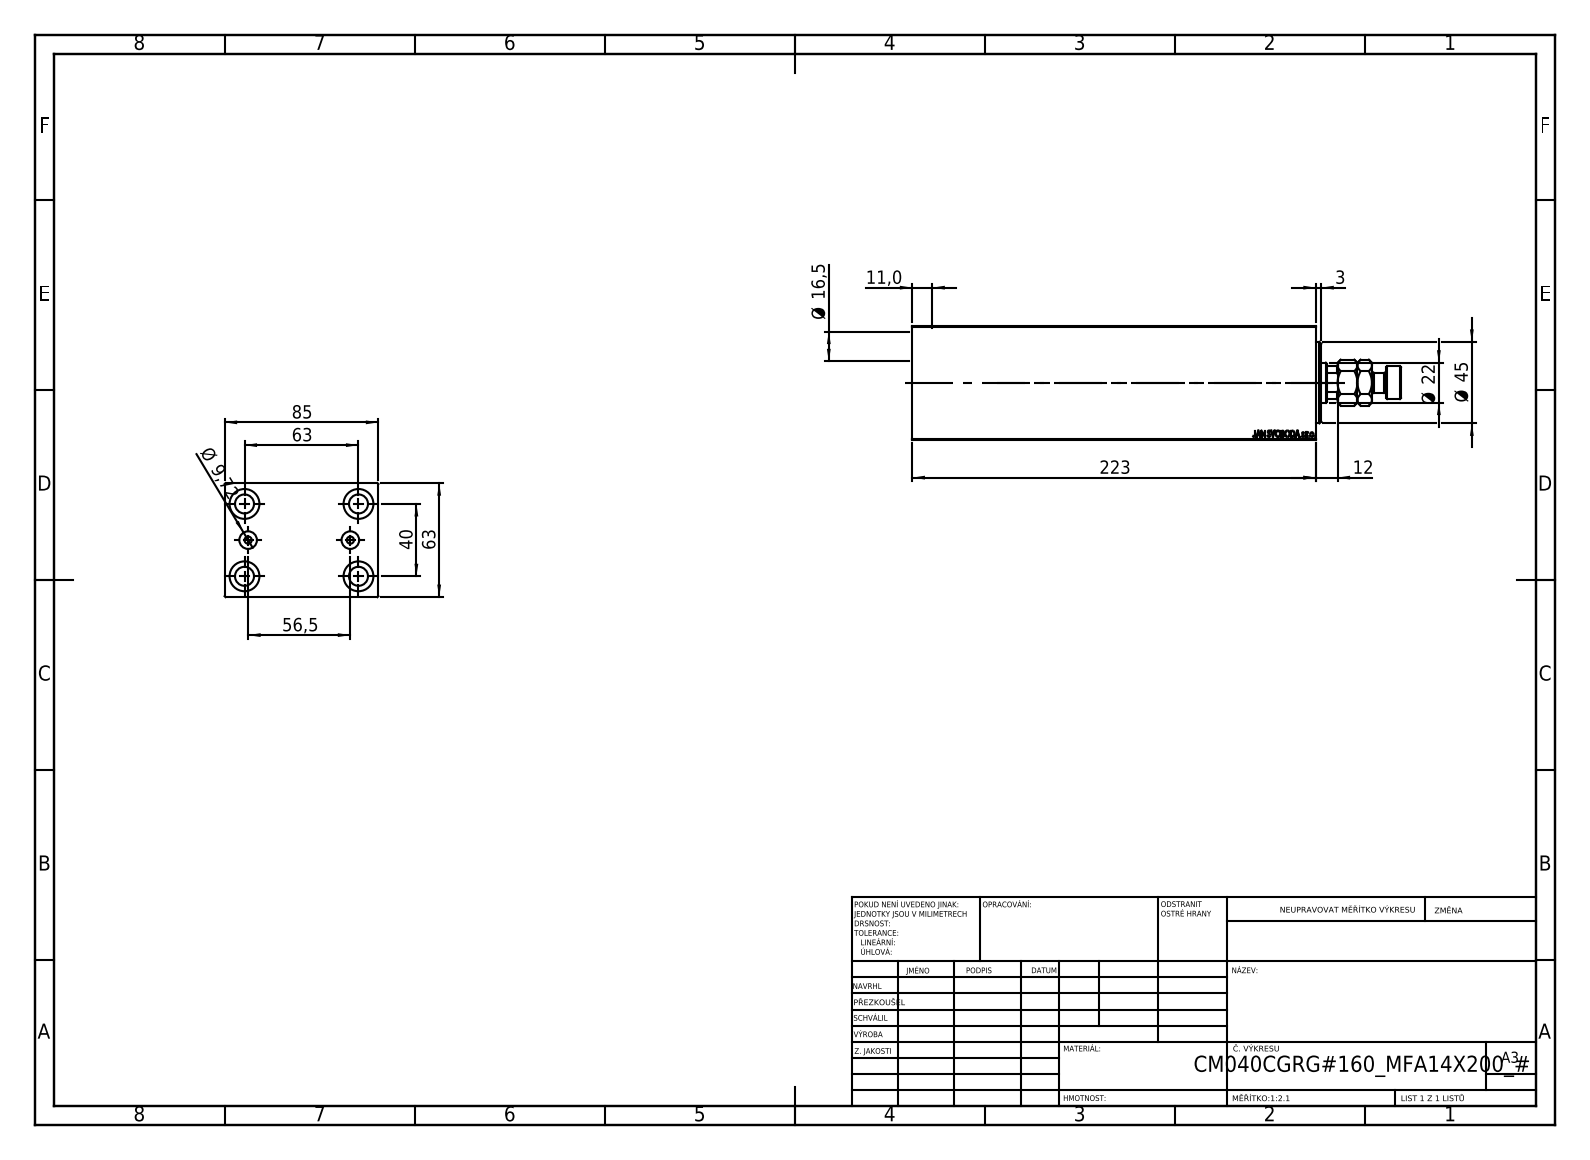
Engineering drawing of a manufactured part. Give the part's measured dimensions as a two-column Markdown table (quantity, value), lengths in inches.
| quantity | value |
| --- | --- |
| part name | V450CM_C_VCP; V450CM_VC_B; V450CM_C_Body; MFA |
| STEP written by | SolidWorks 2019 (CONFIG_CONTROL_DESIGN) |
| units | inches |
| bodies | 4 solids, 910 faces (424 planar, 60 cylindrical, 426 other) |
| overall size | 10.63 × 3.346 × 2.48 |
| volume | 59.45 in³ |
| surface area | 261.8 in² |
| round holes (diameter × count) | 0.413 × 4, 0.65 × 4, 0.157 × 2, 0.383 × 2, 0.492 × 1, 0.866 × 1, 1.004 × 1, 1.575 × 1, 1.654 × 1, 1.772 × 1 |
| round bosses / shafts (diameter × count) | 0.709 × 1, 0.433 × 1 |
| partial cylindrical surfaces (radius × count) | 0.413 × 1 |
| main face-to-face distances | 2.48, 3.346, 0.472, 8.307, 8.78, 0.039, 7.835, 0.433, 8.346, 7.874 |
| hole center spacings | 1.469, 0.791, 0.807, 1.575, 2.434, 2.48, 2.528, 2.938 |
